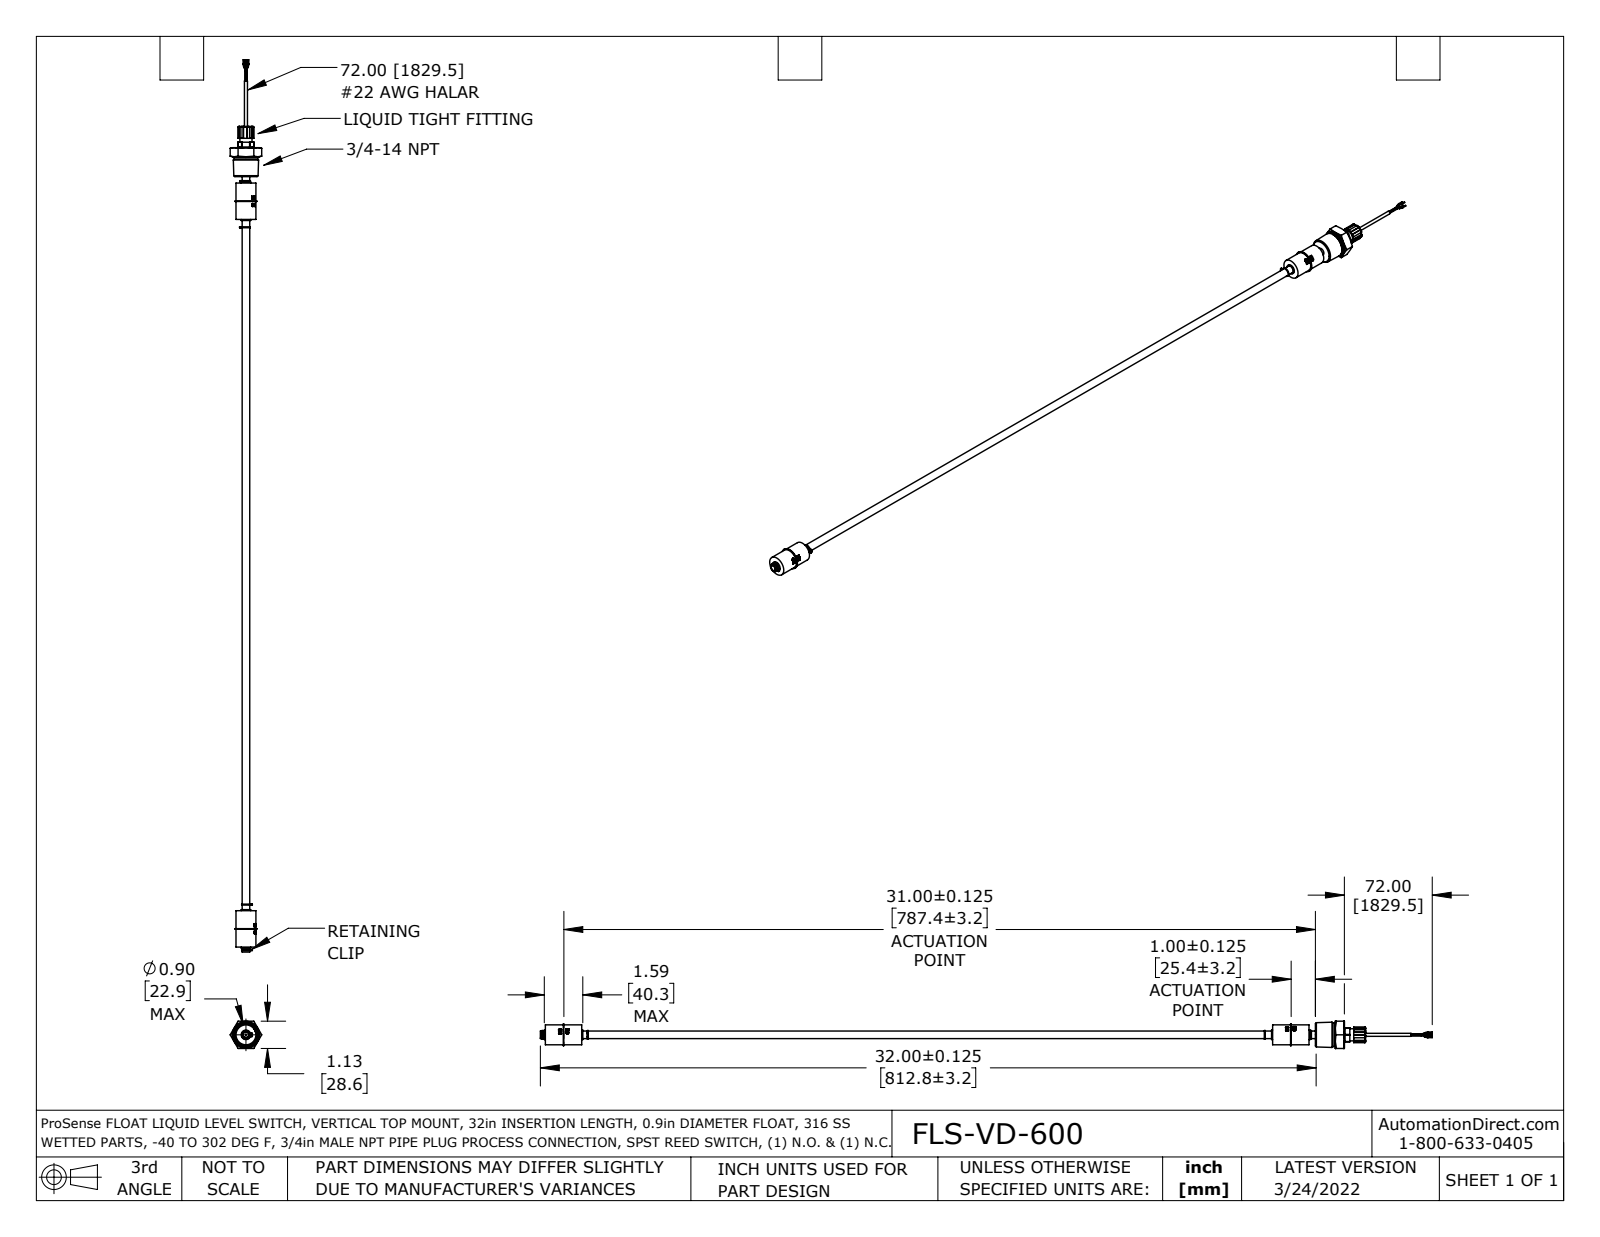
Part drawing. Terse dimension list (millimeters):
name: ADM4169-3 coord fxt
written by: SolidWorks 2021 (AUTOMOTIVE_DESIGN)
unit: mm
bodies: 13 solids, 396 faces (127 planar, 177 cylindrical, 92 other)
size: 934.5 × 33 × 28.6
volume: 58 550 mm³; area: 54 710 mm²
holes: 6× ⌀1, 3× ⌀7.4, 1× ⌀6.2, 1× ⌀7.1, 1× ⌀7.9, 1× ⌀8, 1× ⌀8.9
bosses: 12× ⌀0.8, 2× ⌀9, 1× ⌀24.6, 1× ⌀22.9, 1× ⌀20.9, 1× ⌀12.7, 1× ⌀10, 1× ⌀8.4
rounds: 16× R0.8, 6× R0.7, 6× R1.2, 1× R7.6, 1× R8.3, 1× R10.6
face distances: 762, 38.1, 28.6, 30.4, 37.1, 75.2, 799.1, 6.7, 44.8, 768.7
hole spacings: 5.6, 5.7, 5.9, 11.3, 2, 2, 5.4, 11.1
